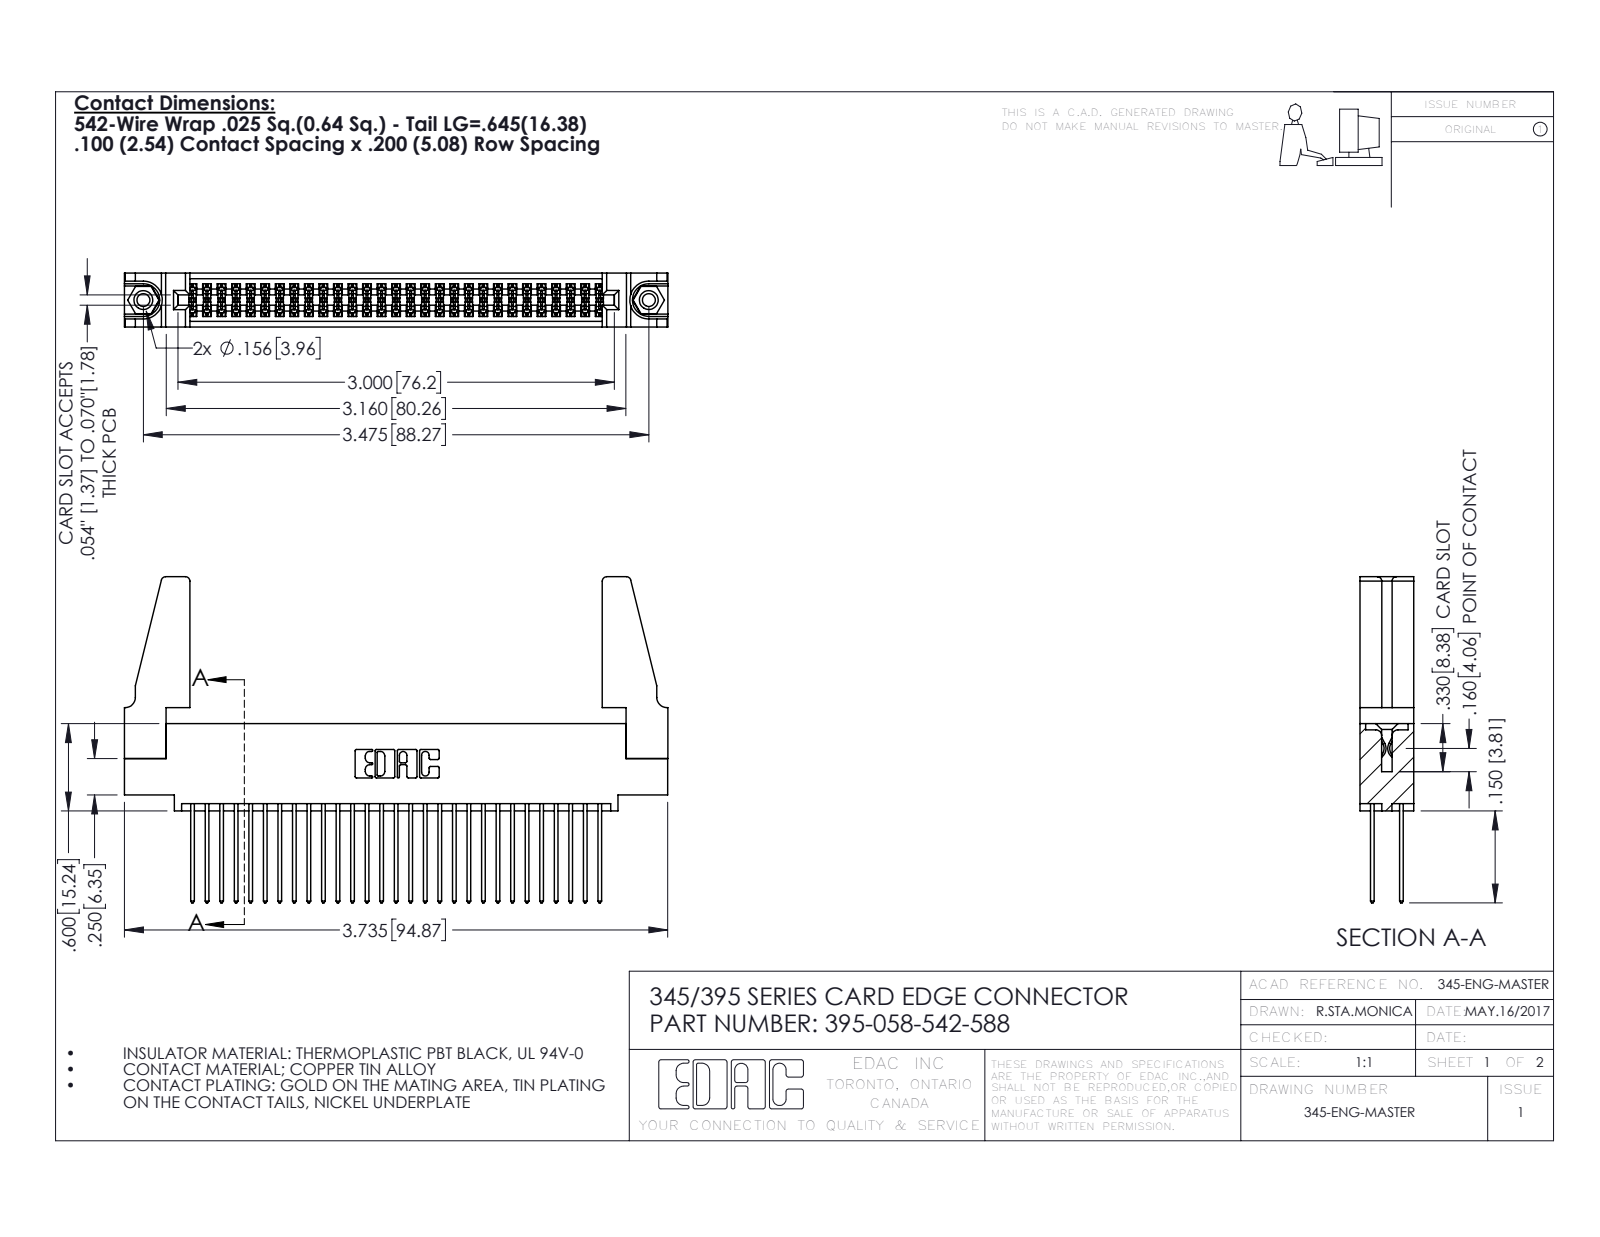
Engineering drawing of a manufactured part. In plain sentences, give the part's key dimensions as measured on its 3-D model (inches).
The part is named "345-292-001_345-293-142; 345 Part_0.110 Offset - 0.156 Dia-TH; 345-250-001_345-250-001-102; 395-058-542-588 (+1 more)". Its 3-D file was written by "SolidWorks 2016 (CONFIG_CONTROL_DESIGN)". It is 63 solids with 3154 faces: 2070 planar, 1068 cylindrical and 16 other. Overall it measures 3.736 by 2.242 by 0.37 inches. Its volume is 0.766 cubic inches and its surface area 27.85 square inches. Round holes: 2 of diameter 0.089, 2 of diameter 0.125, 2 of diameter 0.156, 1 of diameter 0.064. Round bosses or shafts: 2 of diameter 0.155. Partial cylindrical surfaces (rounded edges, fillets, slot ends): 87 of radius 0.006, 58 of radius 0.01, 22 of radius 0.01, 8 of radius 0.03, 6 of radius 0.007, 6 of radius 0.031, 3 of radius 0.026, 2 of radius 0.014. The main face-to-face distances are 0.072, 0.298, 0.37, 0.2, 0.098, 0.272, 0.025, 0.225, 0.175, 0.149. The hole center spacings are 0.27, 3.24, 3.475.
